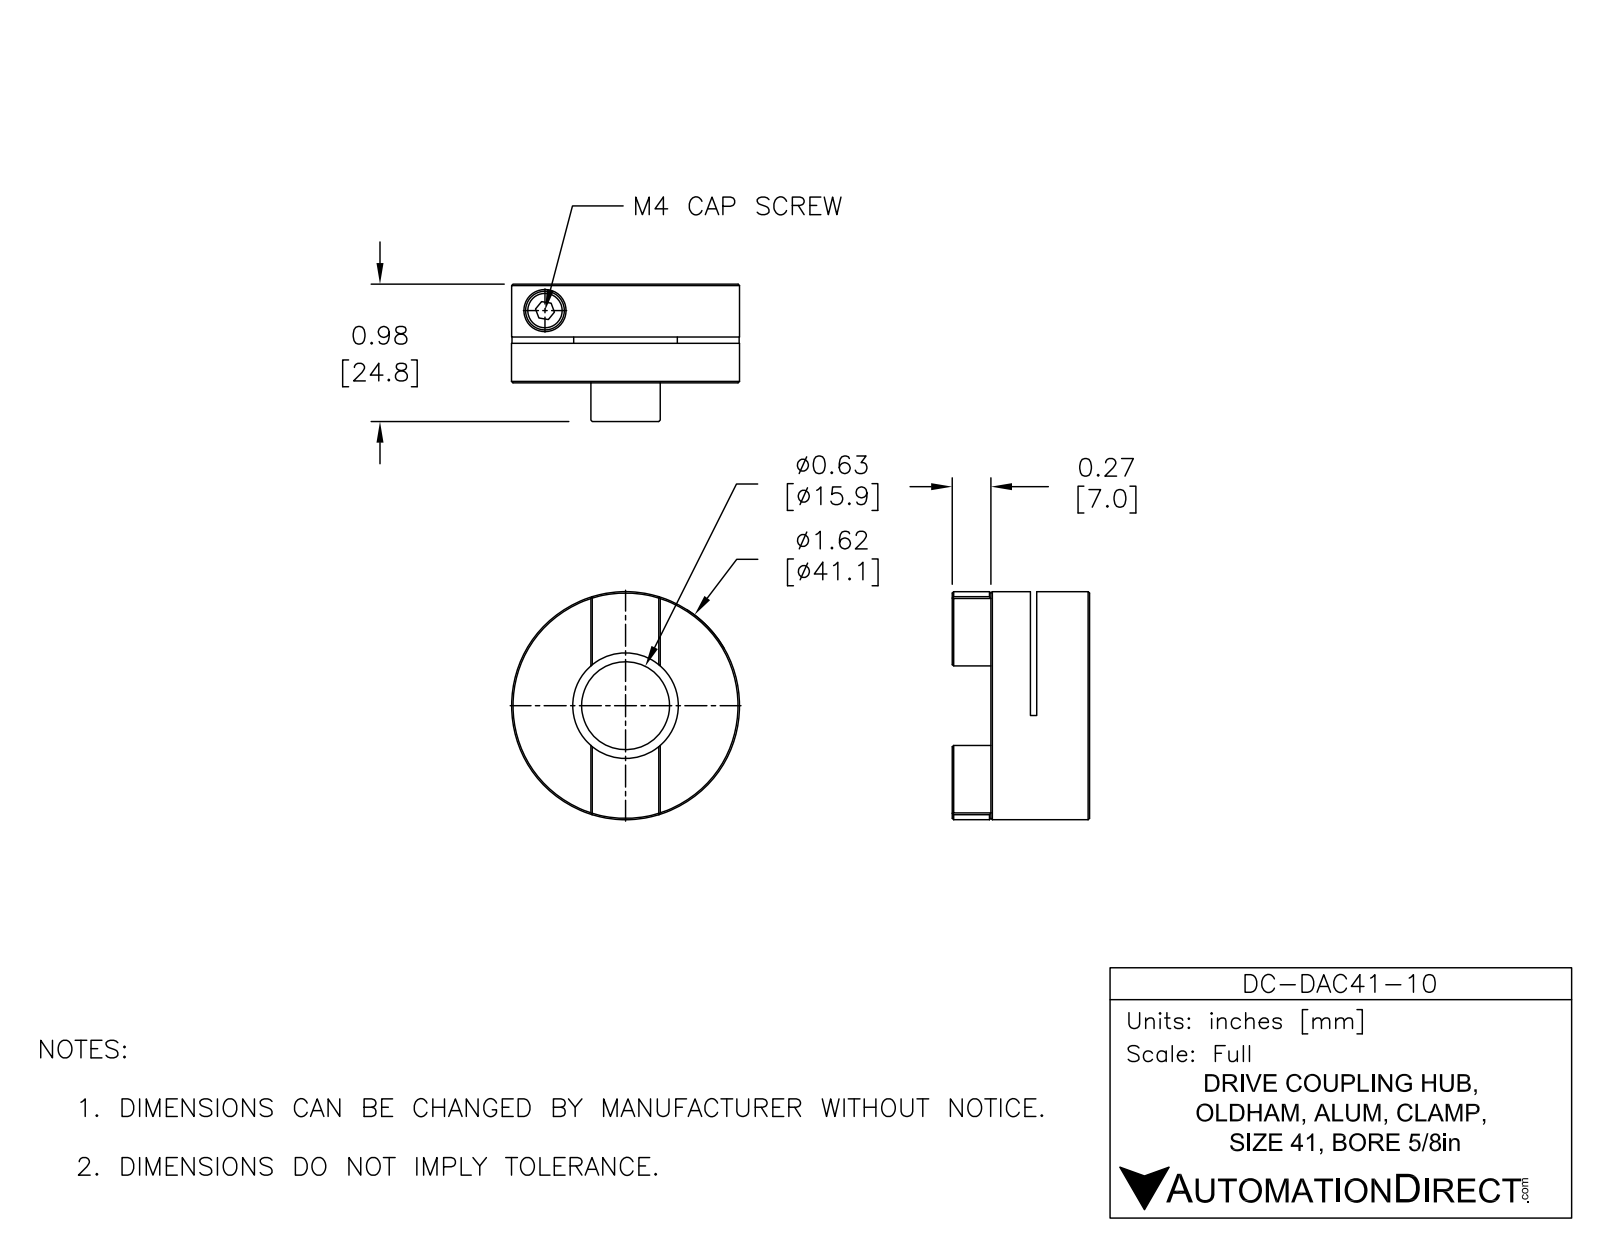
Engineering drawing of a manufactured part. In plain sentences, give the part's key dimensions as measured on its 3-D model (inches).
The part is named "DC-DAC41-10". Its 3-D file was written by "SolidWorks 2015 (AUTOMOTIVE_DESIGN)". It is 1 solid with 52 faces: 27 planar, 15 cylindrical and 10 other. Overall it measures 1.62 by 1.62 by 0.976 inches. Its volume is 1.274 cubic inches and its surface area 12.4 square inches. Round holes: 1 of diameter 0.157, 1 of diameter 0.3, 1 of diameter 0.625. Round bosses or shafts: 1 of diameter 1.62. Partial cylindrical surfaces (rounded edges, fillets, slot ends): 1 of radius 0.875. The main face-to-face distances are 0.701, 0.281, 0.42, 0.326, 0.045, 0.375, 0.274, 0.556, 0.6, 0.975.
